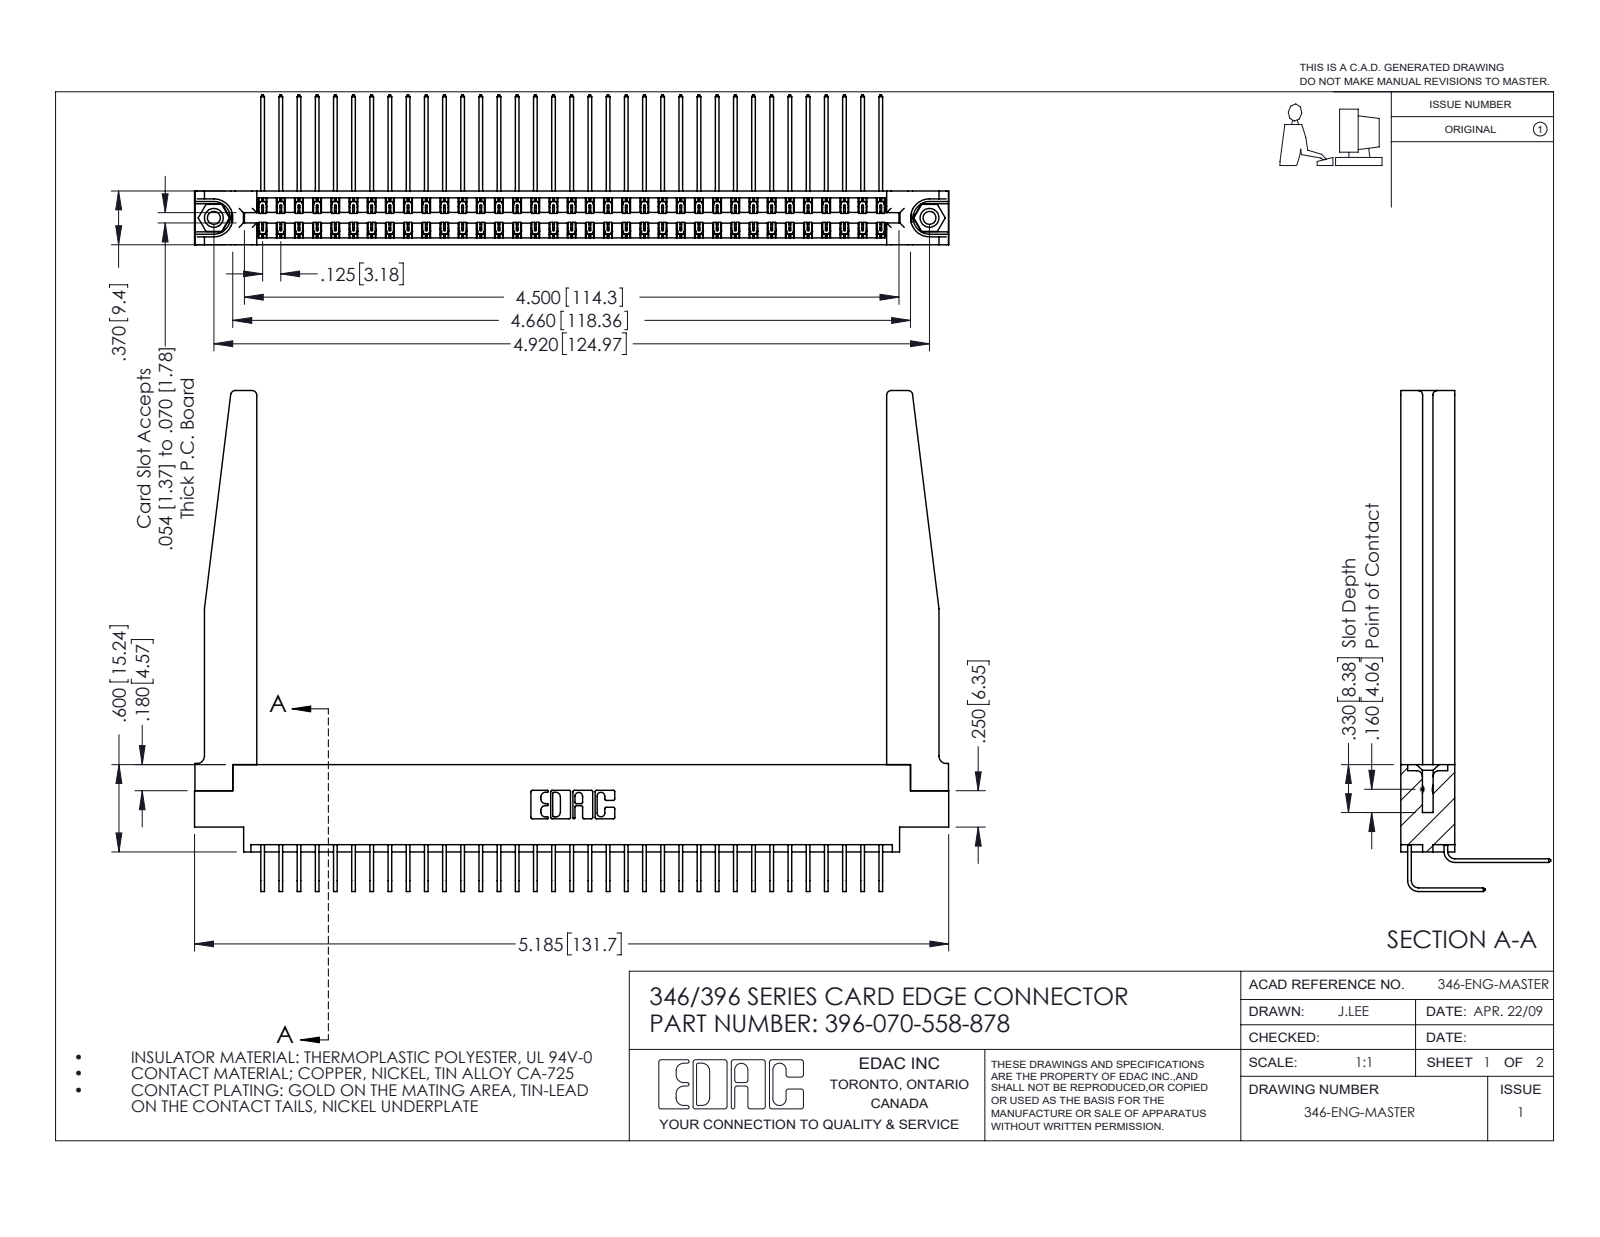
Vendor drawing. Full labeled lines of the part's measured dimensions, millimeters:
Part name (STEP PRODUCT): 346 Part_0.170 Offset - 0.156 Dia-TH; 345-250-001_345-250-001-102; 396-070-558-878; 345-292-001_558 Tail - 2 (+2 more)
STEP written by: SolidWorks 2016 (CONFIG_CONTROL_DESIGN)
Units: millimetres
Bodies: 75 solids, 4140 faces (2812 planar, 1276 cylindrical, 52 other)
Overall size (bounding box): 131.7 × 87.5 × 26.2
Volume: 19 940 mm³ · Surface area: 26 460 mm²
Round holes (diameter × count): ⌀2.3 ×2, ⌀3.2 ×2, ⌀4 ×2, ⌀1.6 ×1
Round bosses / shafts (diameter × count): ⌀3.9 ×2
Partial cylindrical surfaces — rounded edges, fillets, slot ends (radius × count): R0.2 ×105, R0.3 ×22, R0.8 ×8, R0.2 ×6, R0.8 ×6, R1.3 ×4, R0.7 ×3, R0.4 ×2
Main face-to-face distances: 9.4, 8.2, 1.2, 1.8, 0.6, 3.8, 3.8, 7.6, 6.4, 7
Hole centre spacings: 6.2, 119.7, 125
